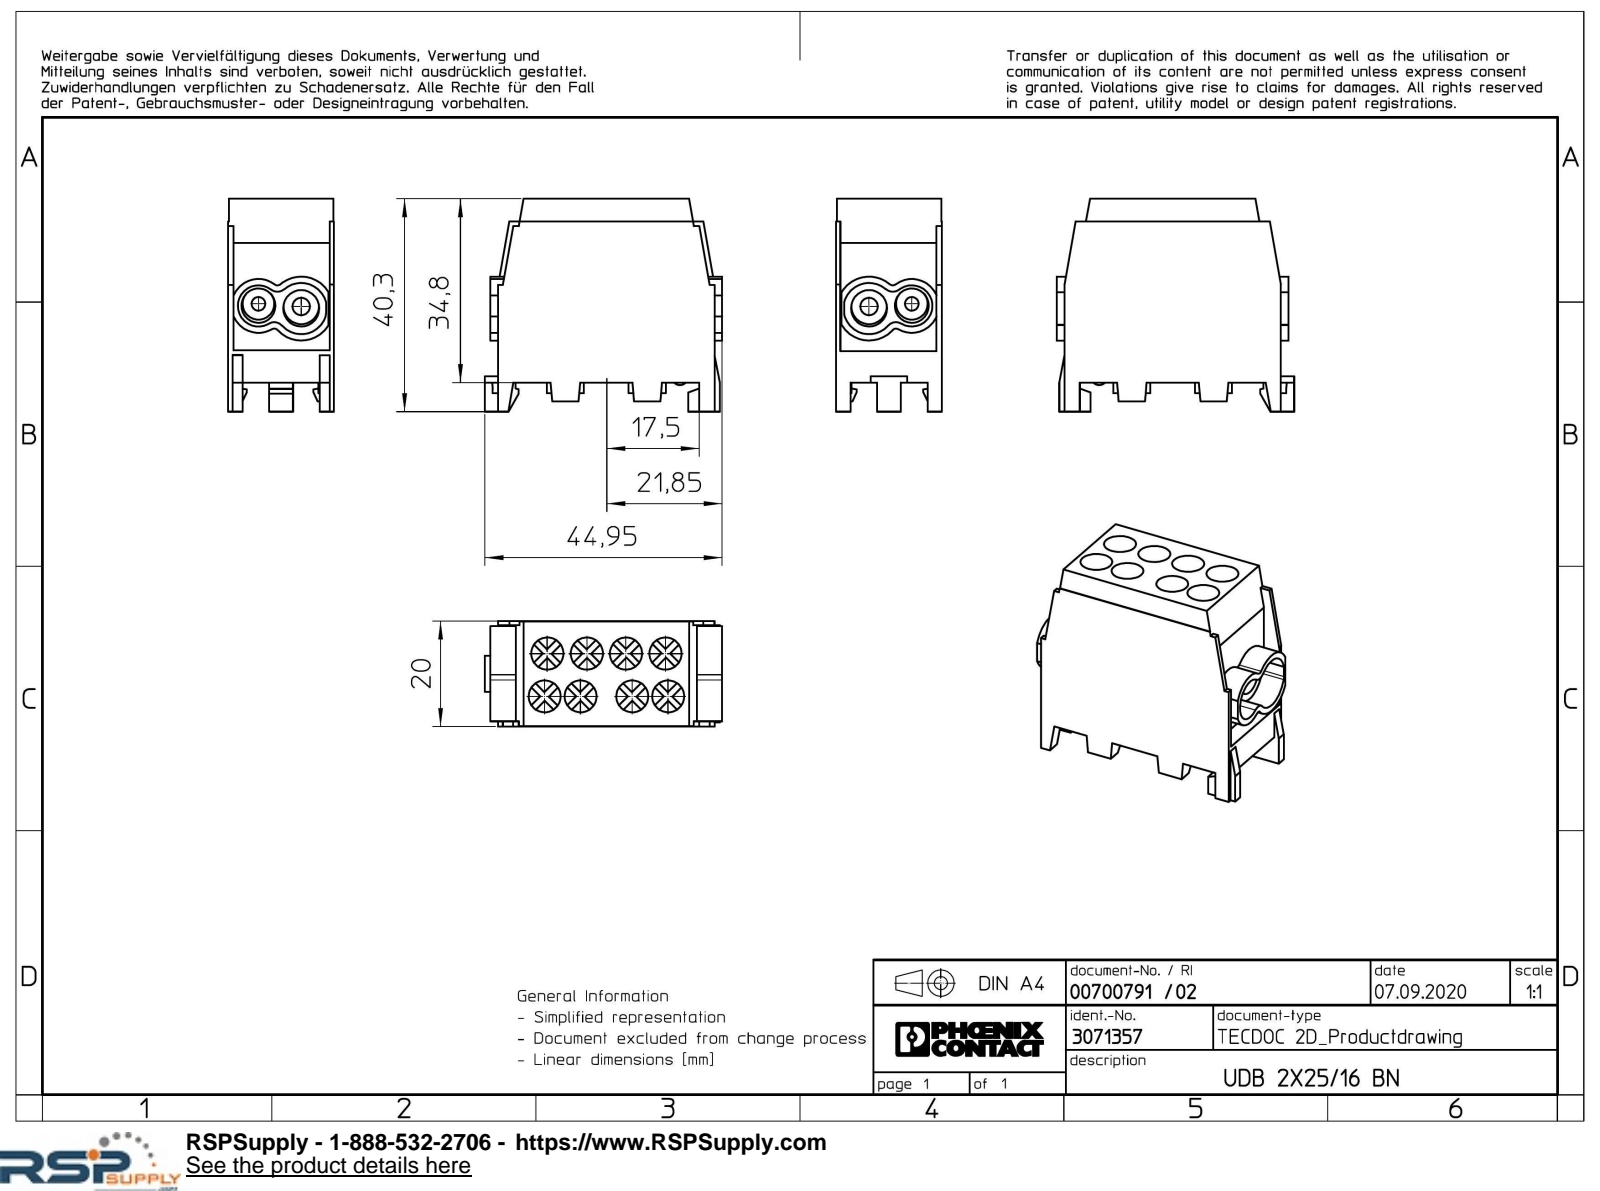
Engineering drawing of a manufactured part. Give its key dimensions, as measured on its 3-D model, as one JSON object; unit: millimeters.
{"part_name": "UDB_2x25_16_BN-select", "step_written_by": "Creo Elements/Direct Modeling 20.1A 29-Sep-2018 (C) Parametric Technology GmbH (AUTOMOTIVE_DESIGN)", "units": "millimeters", "bodies": {"solids": 1, "faces": 309, "planar": 242, "cylindrical": 59, "other": 8}, "overall_size": [44.95, 40.3, 20], "volume_mm3": 22415, "surface_area_mm2": 9855, "round_holes": [[6.05, 4], [6.1, 4], [6, 1], [6.7, 1]], "partial_cylinders_radius": [[0.8, 3], [2, 3], [3.4, 2], [1.5, 1], [3.2, 1], [3.2, 1], [3.9, 1], [4.85, 1]], "face_to_face_distances": [20, 34.8, 3.35, 37.65, 19.9, 34.3, 1, 0.9, 0.8, 0.7], "hole_center_spacings": [6.8, 7.5, 8.12, 8.19, 10.26, 11.38, 11.81, 14.9]}
